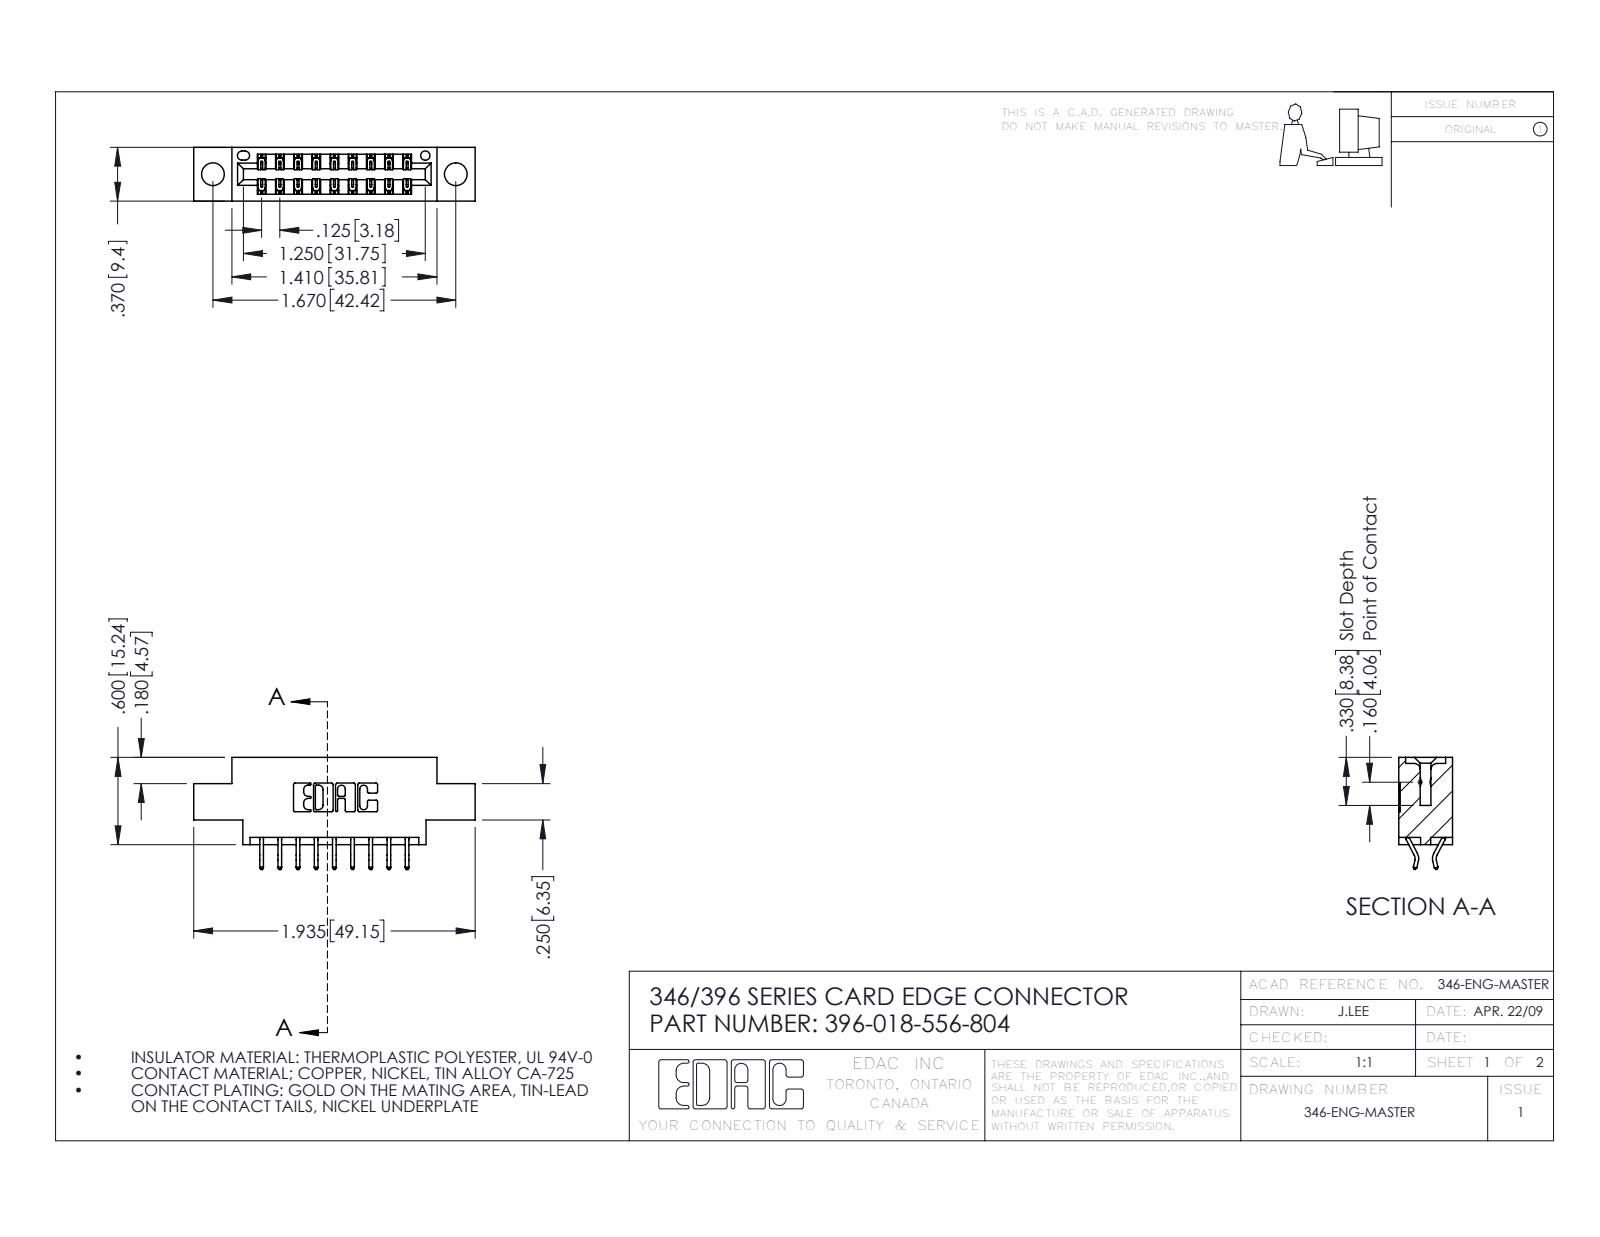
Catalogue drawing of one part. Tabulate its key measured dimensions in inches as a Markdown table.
| quantity | value |
| --- | --- |
| part name | 396-018-556-804; 346 Part_0.170 Offset - 0.156 Dia-TH; 345-292-001_556 Tail |
| STEP written by | SolidWorks 2016 (CONFIG_CONTROL_DESIGN) |
| units | inches |
| bodies | 19 solids, 1170 faces (782 planar, 388 cylindrical, 0 other) |
| overall size | 1.935 × 0.77 × 0.37 |
| volume | 0.262 in³ |
| surface area | 8.306 in² |
| round holes (diameter × count) | 0.156 × 2, 0.064 × 1 |
| partial cylindrical surfaces (radius × count) | 0.006 × 27, 0.01 × 22, 0.007 × 6, 0.031 × 6, 0.026 × 3, 0.01 × 2, 0.014 × 2, 0.022 × 2 |
| main face-to-face distances | 0.25, 0.37, 0.048, 0.322, 0.025, 0.148, 0.222, 0.1, 0.174, 0.072 |
| hole center spacings | 0.246, 1.465, 1.67 |
